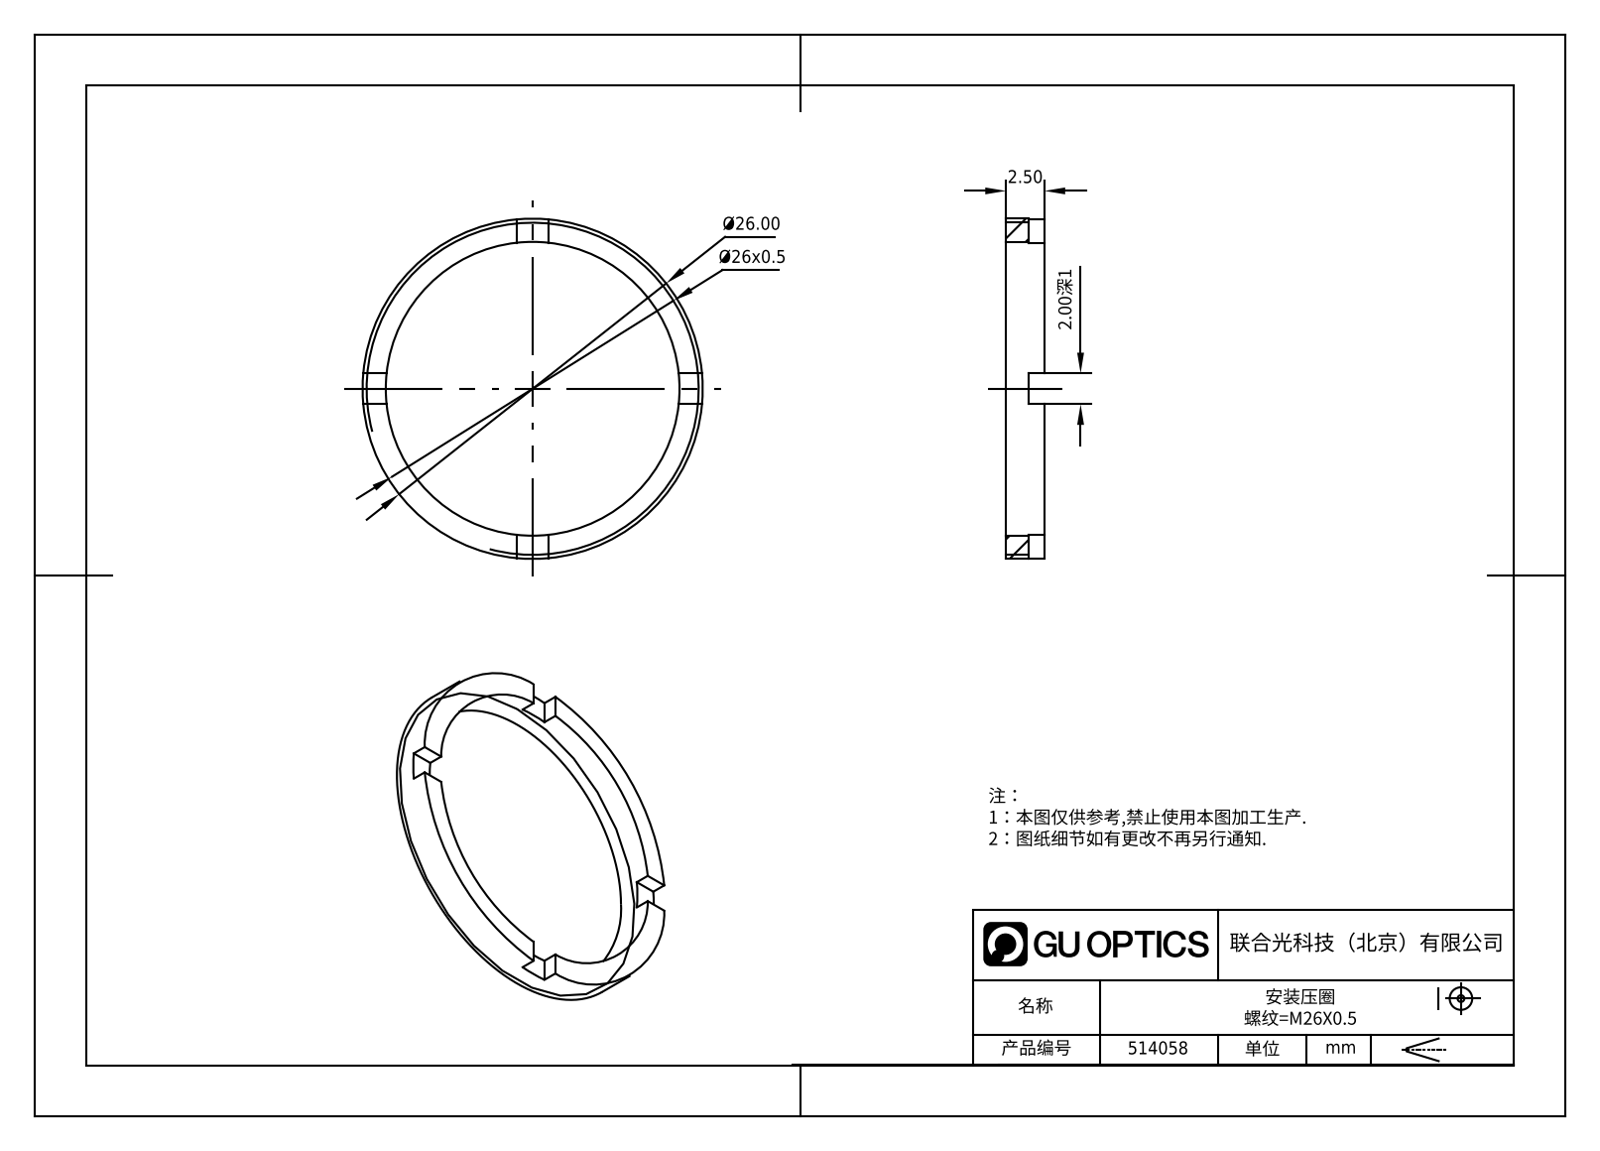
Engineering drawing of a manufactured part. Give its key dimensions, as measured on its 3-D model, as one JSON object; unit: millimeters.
{"part_name": "514058", "step_written_by": "SolidWorks 2020 (CONFIG_CONTROL_DESIGN)", "units": "millimeters", "bodies": {"solids": 1, "faces": 21, "planar": 17, "cylindrical": 4, "other": 0}, "overall_size": [26, 26, 2.5], "volume_mm3": 277, "surface_area_mm2": 612, "round_holes": [[23, 1]], "round_bosses_or_shafts": [[26, 1]], "face_to_face_distances": [2.5, 1.5, 1, 2]}
